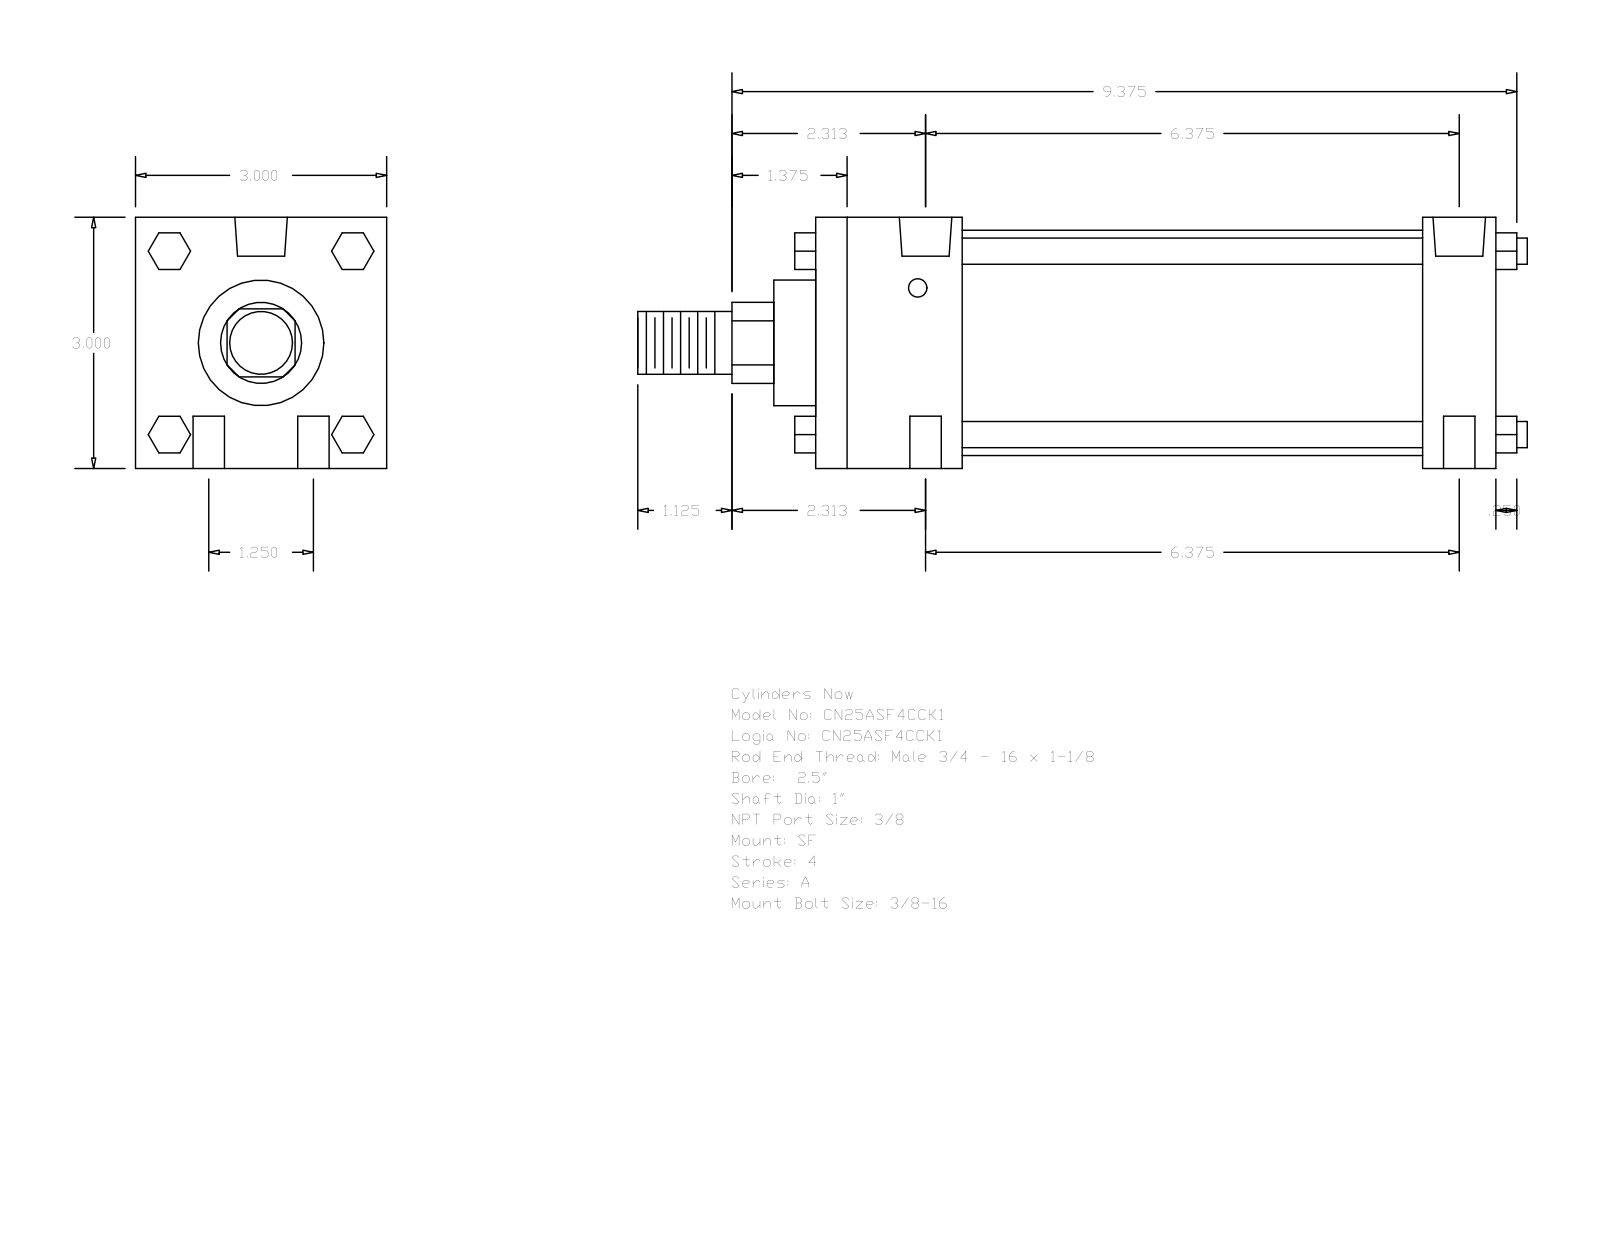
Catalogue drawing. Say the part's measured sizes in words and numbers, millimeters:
The part is named "A_SF__0250_1". Its 3-D file was written by "GSSL Pune (CONFIG_CONTROL_DESIGN)". It is 0 solids with 124 faces: 94 planar, 30 cylindrical and 0 other. Overall it measures 269.88 by 76.2 by 76.2 millimeters. Round holes: 4 of diameter 9.53, 2 of diameter 5.56, 2 of diameter 15.93. Round bosses or shafts: 4 of diameter 7.94, 1 of diameter 68.33, 1 of diameter 38.1, 1 of diameter 25.4, 1 of diameter 19.05. Partial cylindrical surfaces (rounded edges, fillets, slot ends): 1 of radius 12.29. The main face-to-face distances are 76.2, 206.38, 184.15, 22.23, 44.45, 139.7, 161.93, 12.7, 11.11, 57.15. The hole center spacings are 15.88, 162.7, 161.92, 31.76, 165.01, 166.68.
